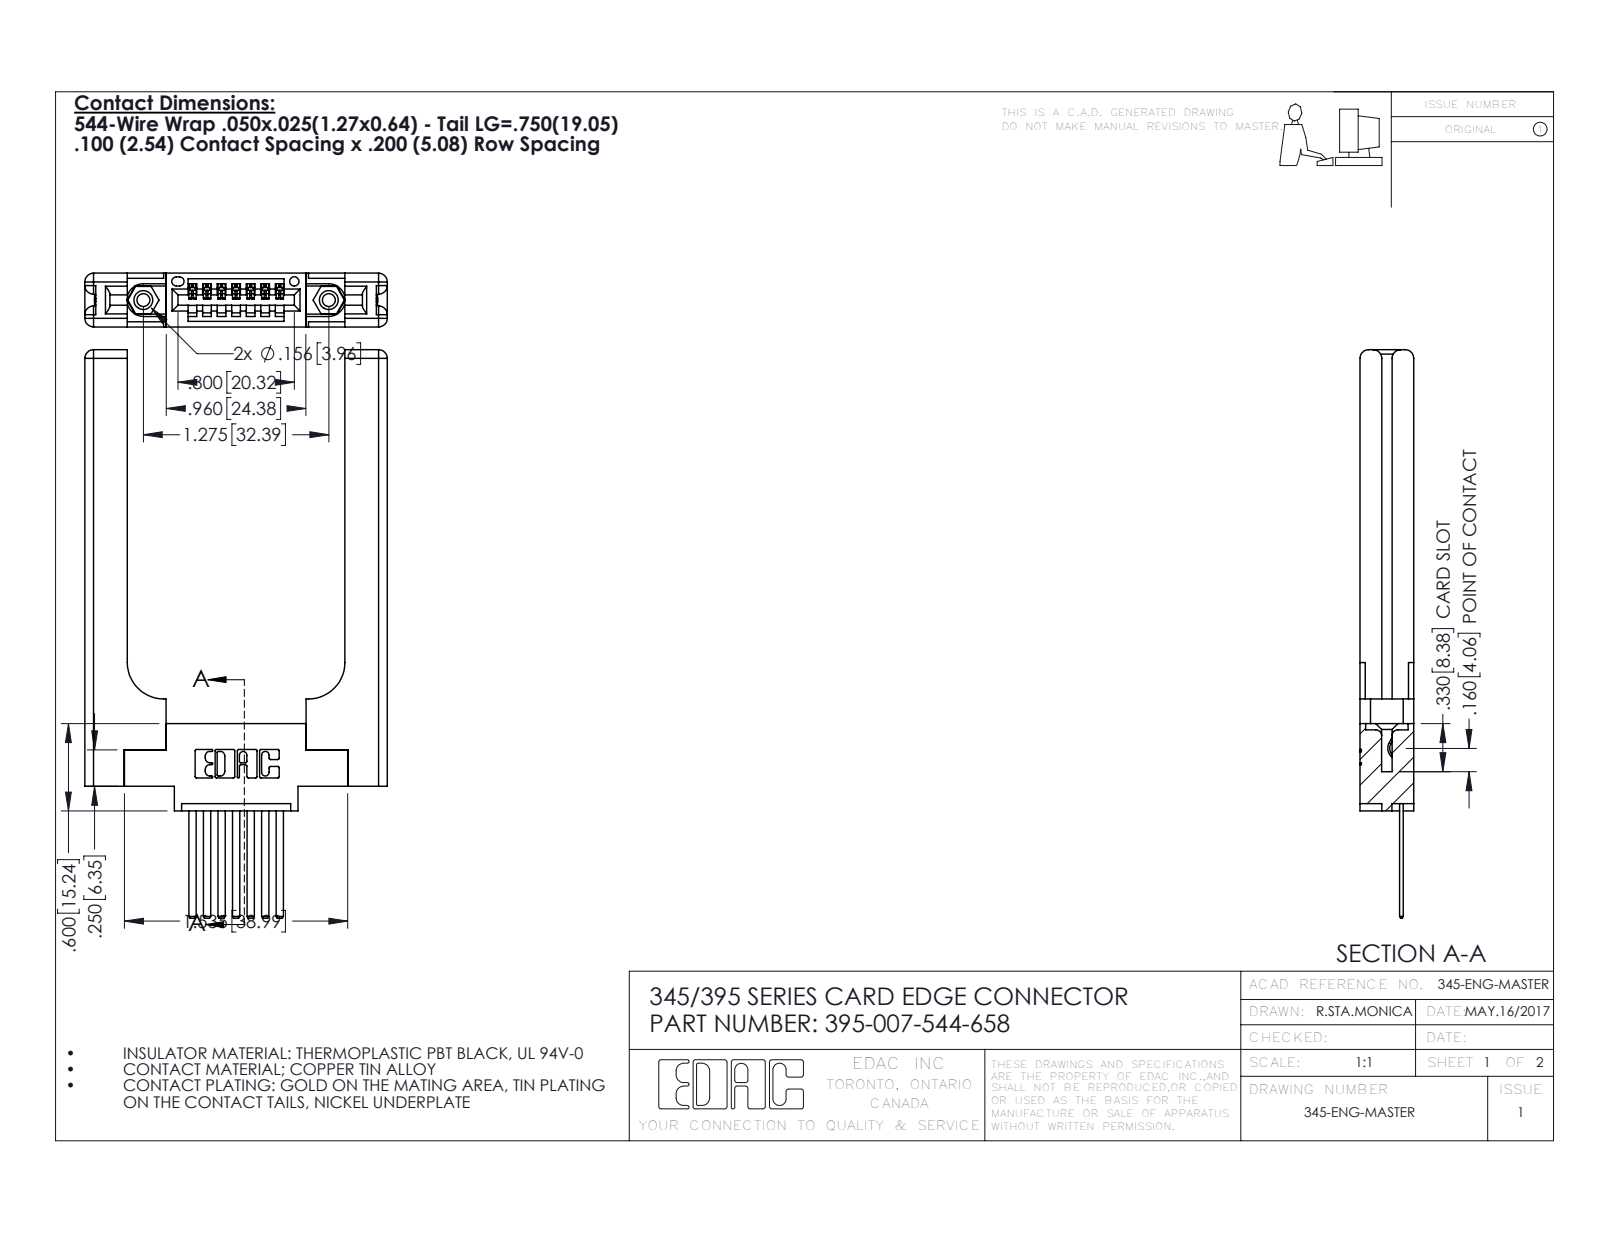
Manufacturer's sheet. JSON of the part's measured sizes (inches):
{"part_name": "345 Part_0.170 Offset - 0.156 Dia-TH; 395-007-544-658; 345-220-058_345-220-058; 345-292-001_345-293-144 (+1 more)", "step_written_by": "SolidWorks 2016 (CONFIG_CONTROL_DESIGN)", "units": "inches", "bodies": {"solids": 12, "faces": 750, "planar": 484, "cylindrical": 206, "other": 60}, "overall_size": [3.907, 2.079, 0.37], "volume_in3": 0.806, "surface_area_in2": 17.73, "round_holes": [[0.089, 2], [0.125, 2], [0.156, 2], [0.064, 1]], "round_bosses_or_shafts": [[0.155, 2]], "partial_cylinders_radius": [[0.01, 22], [0.06, 16], [0.006, 14], [0.007, 6], [0.031, 6], [0.026, 3], [0.03, 2], [0.031, 2]], "face_to_face_distances": [0.37, 0.15, 0.072, 0.22, 0.298, 0.148, 0.077, 1.496, 0.071, 0.123], "hole_center_spacings": [0.27, 1.045, 1.275]}
